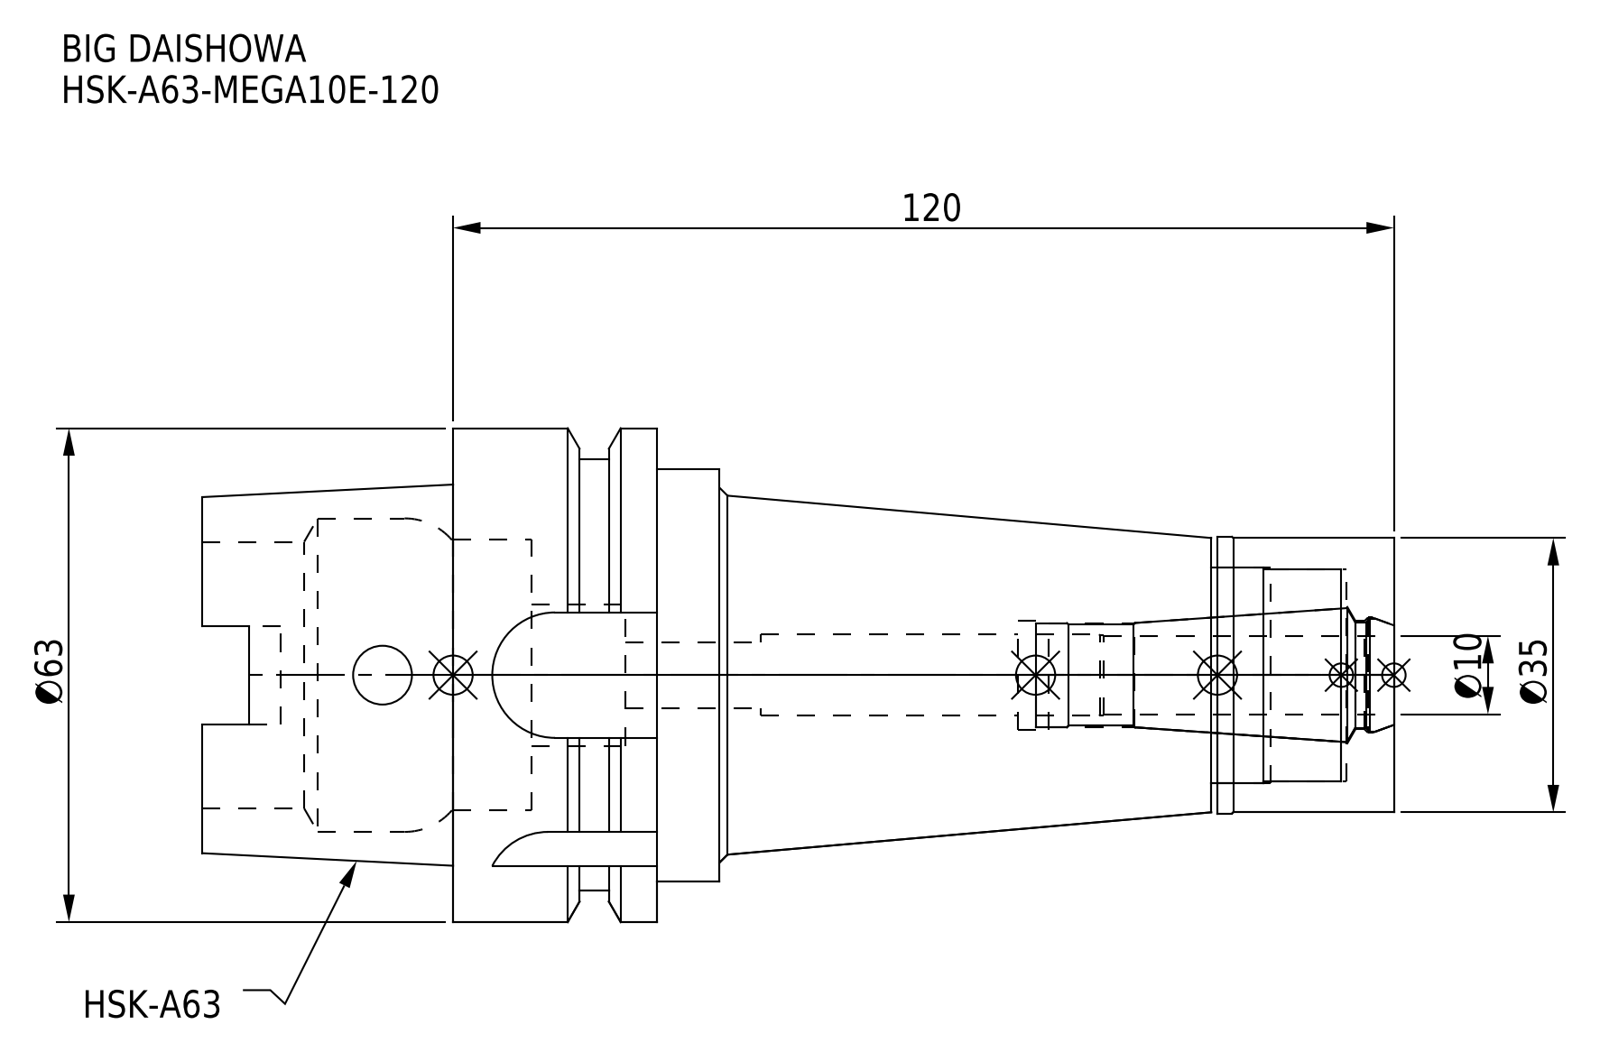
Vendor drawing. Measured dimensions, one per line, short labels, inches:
name: HSK-A63-MEGA10E-120-100.stp; HSK-A63-MEGA10E-120; MEN10_1.stp; DXF_TEMP_ASSY_ASM_4_ASM.stp (+3 more)
written by: SolidWorks 2019 (CONFIG_CONTROL_DESIGN)
unit: in
bodies: 2 solids, 127 faces (45 planar, 54 cylindrical, 28 other)
size: 5.984 × 2.48 × 2.48
volume: 11.64 in³; area: 64.08 in²
holes: 1× ⌀0.295, 1× ⌀0.331, 1× ⌀0.409, 1× ⌀0.524, 1× ⌀0.543, 1× ⌀0.547, 1× ⌀0.579, 1× ⌀0.709, 1× ⌀1.063, 1× ⌀1.083, 1× ⌀1.339, 1× ⌀1.358
bosses: 1× ⌀2.48, 1× ⌀2.165, 1× ⌀2.071, 1× ⌀1.39, 1× ⌀1.378
rounds: 2× R0.11, 2× R0.113, 2× R0.315, 1× R0.354
face distances: 1.024, 3.701, 4.724, 4.333, 0.632, 0.392, 5.984, 2.283, 1.652, 1.26
